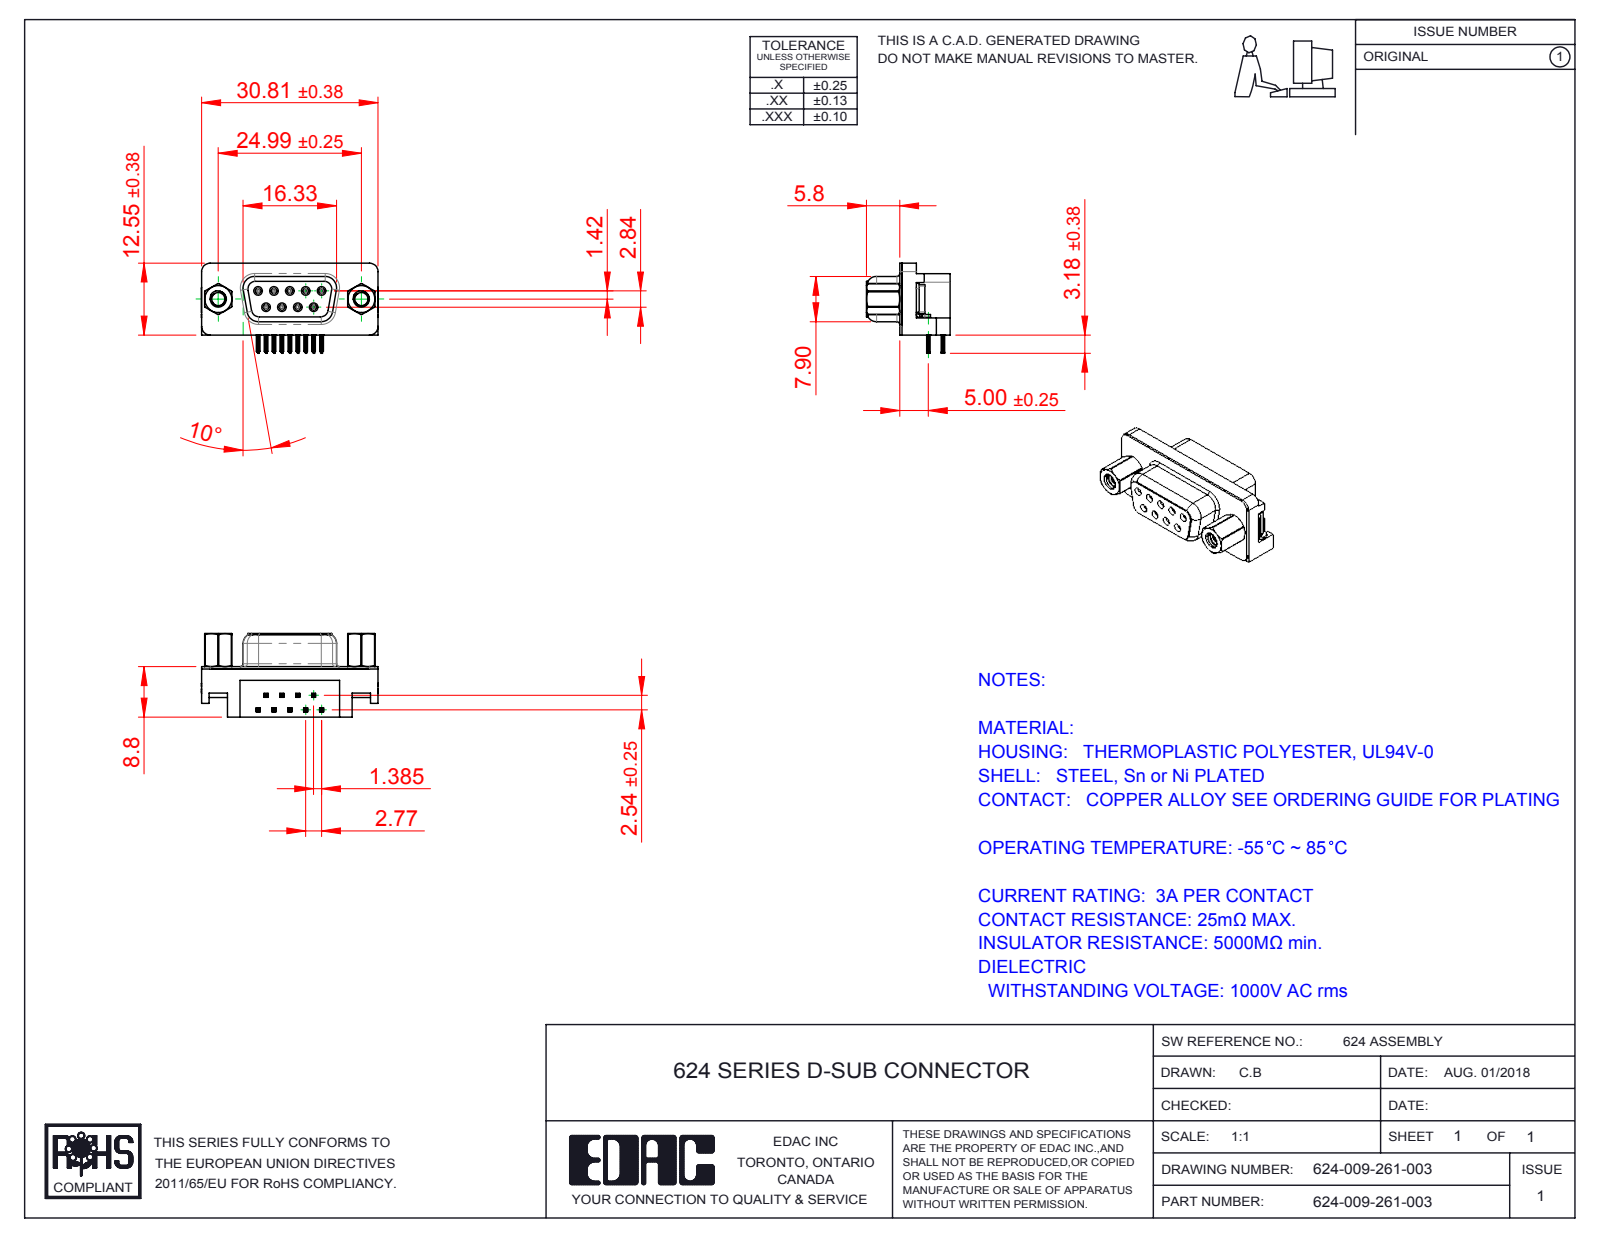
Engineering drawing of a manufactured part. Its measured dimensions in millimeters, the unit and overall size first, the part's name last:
Units: millimetres
Overall size (bounding box): 30.89 × 15.73 × 14.6
Round holes (diameter × count): ⌀0.8 ×9, ⌀0.9 ×9, ⌀2.26 ×2, ⌀2.29 ×2, ⌀4 ×2, ⌀4.8 ×2, ⌀5 ×2
Round bosses / shafts (diameter × count): ⌀1.2 ×9, ⌀4.9 ×2, ⌀4.75 ×2, ⌀3.9 ×2, ⌀2.79 ×2
Partial cylindrical surfaces — rounded edges, fillets, slot ends (radius × count): R0.1 ×72, R0.15 ×36, R0.35 ×18, R1 ×18, R0.34 ×9, R0.25 ×8, R1.35 ×8, R1.5 ×7
Main face-to-face distances: 0.4, 8.4, 8.8, 2.9, 6.2, 2.5, 5.9, 0.35, 5.8, 10.69
Hole centre spacings: 3.16, 2.77, 5.54, 5.03, 5.04, 8.31, 7.48, 7.49
Volume: 3 146 mm³ · Surface area: 4 805 mm²
Bodies: 17 solids, 1644 faces (664 planar, 474 cylindrical, 506 other)
Part name (STEP PRODUCT): 624-009-261-003; 624 4-40 Hex Standoff 5; 624 4-40 Threaded Rivet; 624 Non Board Mount (+4 more)
STEP written by: SolidWorks 2016 (CONFIG_CONTROL_DESIGN)
